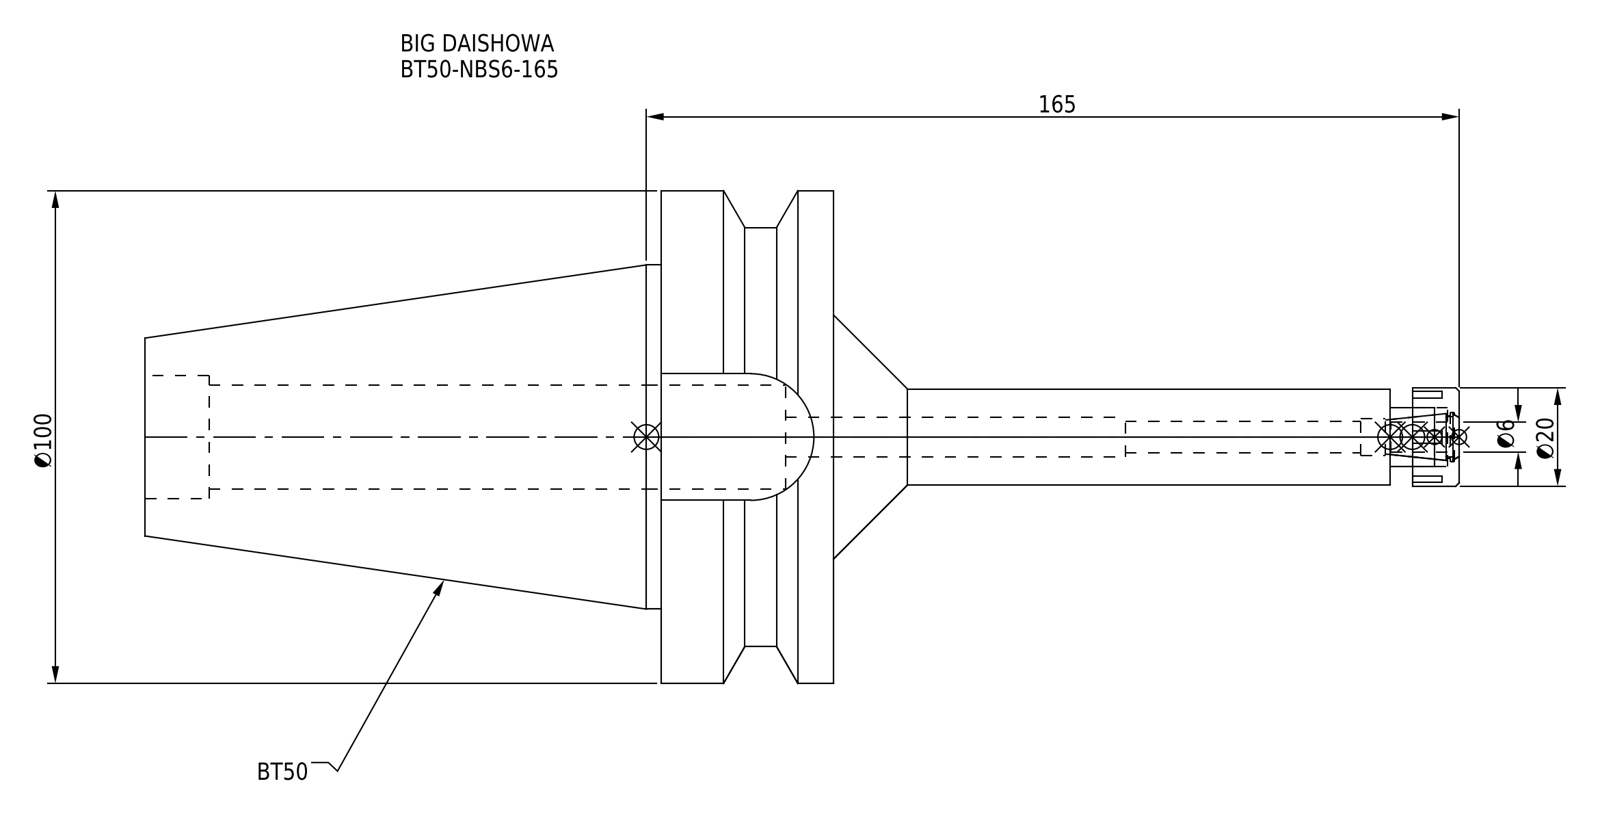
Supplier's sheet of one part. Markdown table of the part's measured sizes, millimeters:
| quantity | value |
| --- | --- |
| part name | DXF_TEMP_ASSY_ASM_4_ASM.stp; BT50-NBS6-165; BT50-NBS6-165-FreeParts; BT50NB06165-060_ASM.stp (+3 more) |
| STEP written by | SolidWorks 2019 (CONFIG_CONTROL_DESIGN) |
| units | millimeters |
| bodies | 2 solids, 93 faces (45 planar, 34 cylindrical, 14 other) |
| overall size | 266.8 × 100 × 100 |
| volume | 487 690 mm³ |
| surface area | 65 525 mm² |
| round holes (diameter × count) | 6.4 × 1, 7.5 × 1, 8 × 1, 8.5 × 1, 10 × 1, 12 × 1, 21.2 × 1, 25 × 1 |
| round bosses / shafts (diameter × count) | 100 × 1, 85 × 1, 69.85 × 1, 20 × 1, 19.5 × 1 |
| partial cylindrical surfaces (radius × count) | 12.85 × 1 |
| main face-to-face distances | 35, 139.8, 104.8, 70.8, 25.7, 9.8, 25.2, 130, 4.5, 127 |
